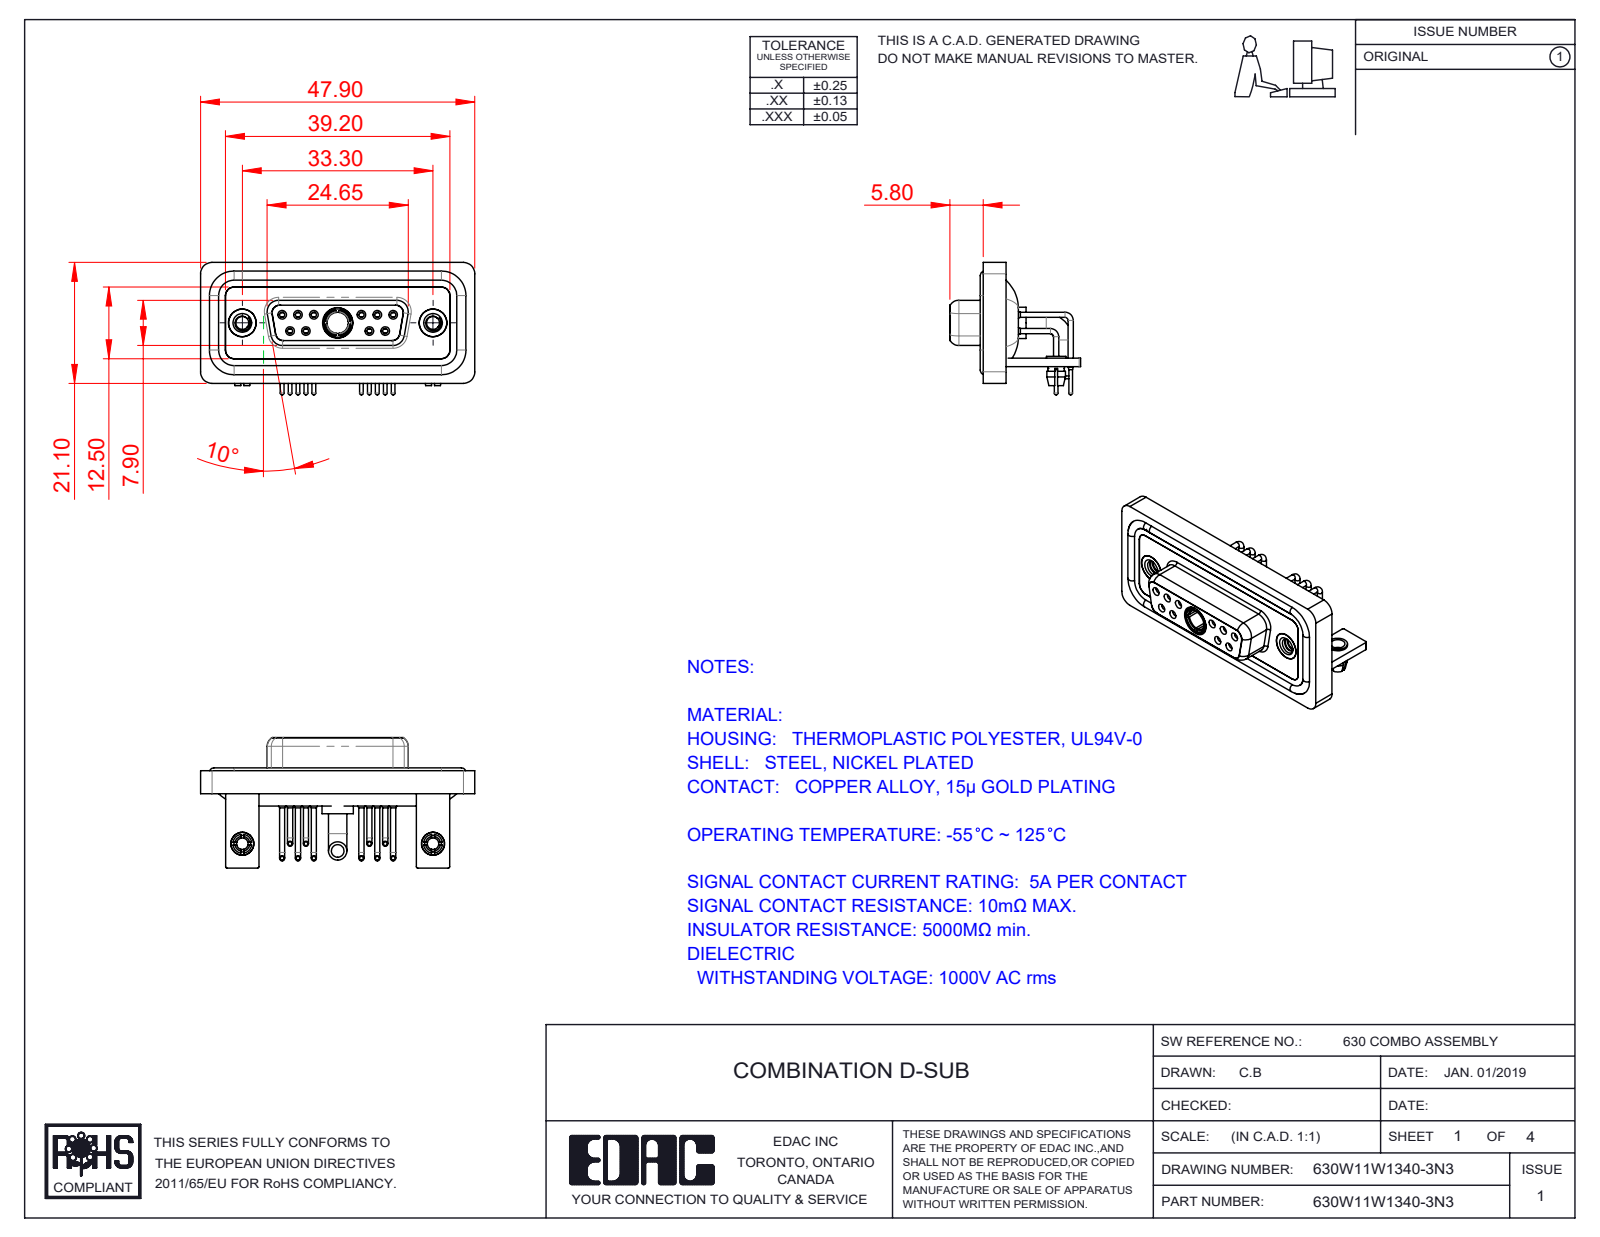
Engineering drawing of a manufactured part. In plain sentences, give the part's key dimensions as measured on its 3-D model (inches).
The part is named "630Combo Shell Front_15 Contacts; 630Combo Board Lock_50 Contacts; 630Combo Stabilizer Bracket_50 Contacts; 630Combo Housing_11W1 (+7 more)". Its 3-D file was written by "SolidWorks 2023 (CONFIG_CONTROL_DESIGN)". It is 23 solids with 1134 faces: 352 planar, 499 cylindrical and 283 other. Overall it measures 1.886 by 0.91 by 0.898 inches. Its volume is 0.406 cubic inches and its surface area 17.72 square inches. Round holes: 12 of diameter 0.079, 10 of diameter 0.035, 10 of diameter 0.043, 10 of diameter 0.059, 6 of diameter 0.067, 4 of diameter 0.063, 3 of diameter 0.191, 2 of diameter 0.089, 2 of diameter 0.098, 2 of diameter 0.126, 2 of diameter 0.157, 2 of diameter 0.159. Round bosses or shafts: 10 of diameter 0.063, 10 of diameter 0.035, 10 of diameter 0.026, 2 of diameter 0.195, 2 of diameter 0.189, 2 of diameter 0.157, 2 of diameter 0.134, 2 of diameter 0.13. Partial cylindrical surfaces (rounded edges, fillets, slot ends): 21 of radius 0.079, 18 of radius 0.059, 16 of radius 0.01, 12 of radius 0.053, 8 of radius 0.063, 5 of radius 0.02, 4 of radius 0.024, 4 of radius 0.026. The main face-to-face distances are 0.016, 0.114, 0.059, 0.071, 0.146, 0.043, 0.063, 0.161, 0.031, 0.098. The hole center spacings are 0.124, 0.109, 0.545, 0.436, 0.654, 0.198, 0.198, 0.218.
